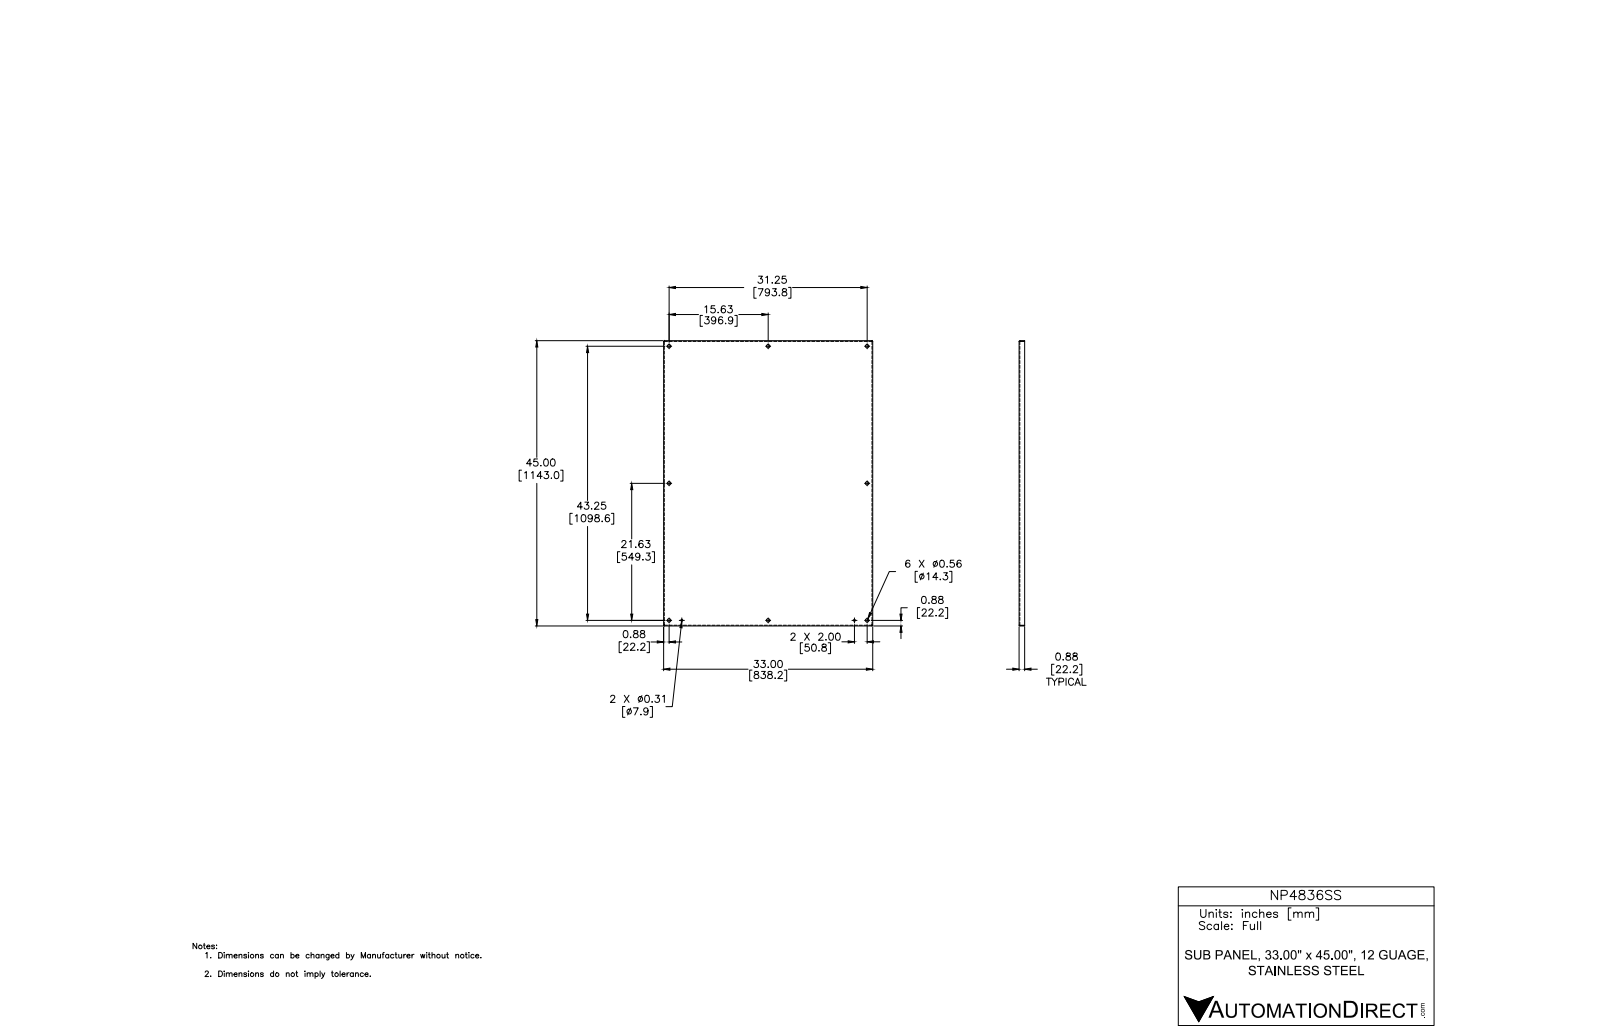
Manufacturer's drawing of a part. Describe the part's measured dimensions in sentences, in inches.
The part is named "NP4836SS". Its 3-D file was written by "Autodesk Inventor 2012 (AUTOMOTIVE_DESIGN)". It is 1 solid with 48 faces: 22 planar, 18 cylindrical and 8 other. Overall it measures 45 by 33 by 0.875 inches. Its volume is 149.8 cubic inches and its surface area 3 214 square inches. Round holes: 8 of diameter 0.563, 2 of diameter 0.312. Partial cylindrical surfaces (rounded edges, fillets, slot ends): 4 of radius 0.031, 4 of radius 0.125. The main face-to-face distances are 0.094, 32.906, 44.906, 32.813, 33, 45, 44.813, 0.781, 0.875, 0.105. The hole center spacings are 45.986, 38.003, 43.25, 15.625, 15.625, 21.625, 21.625, 21.717.
